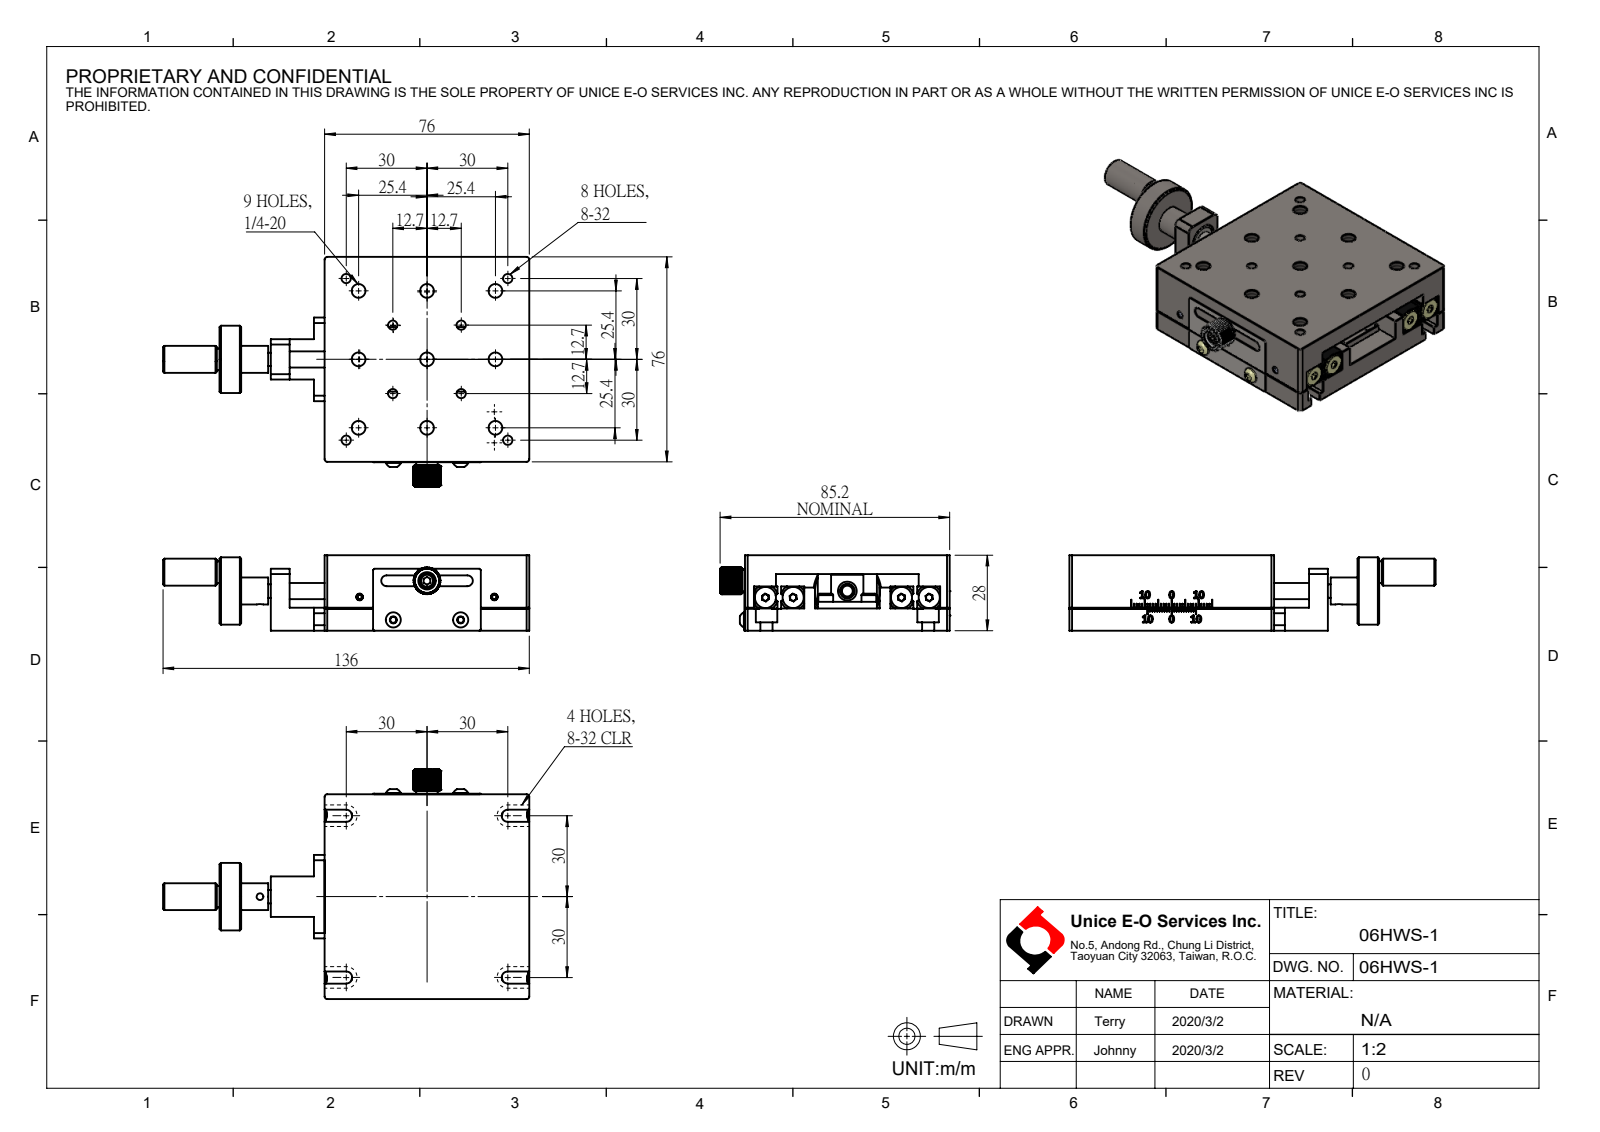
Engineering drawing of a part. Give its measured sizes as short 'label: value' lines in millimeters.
name: 06HWS-1
written by: SolidWorks 2022 (CONFIG_CONTROL_DESIGN)
unit: mm
bodies: 58 solids, 1672 faces (1134 planar, 272 cylindrical, 266 other)
size: 136 × 86.1 × 28
volume: 138 793 mm³; area: 73 206 mm²
holes: 28× ⌀2.5, 16× ⌀3.5, 15× ⌀6, 9× ⌀5.11, 8× ⌀3.45, 6× ⌀3.4, 4× ⌀3.3, 4× ⌀4.5, 4× ⌀6.5, 2× ⌀3, 2× ⌀3.1, 2× ⌀3.2
bosses: 25× ⌀3, 22× ⌀5.5, 4× ⌀7.85, 4× ⌀3.9, 2× ⌀10, 2× ⌀8, 2× ⌀6, 2× ⌀5.6
rounds: 8× R2, 4× R1, 4× R2.25, 4× R4, 1× R5, 1× R10
face distances: 8.2, 28, 19.8, 7, 12.8, 4.6, 21, 11.6, 16.4, 76
hole spacings: 25.4, 17.96, 40.16, 25, 35.92, 27.52, 50.5, 56.35
